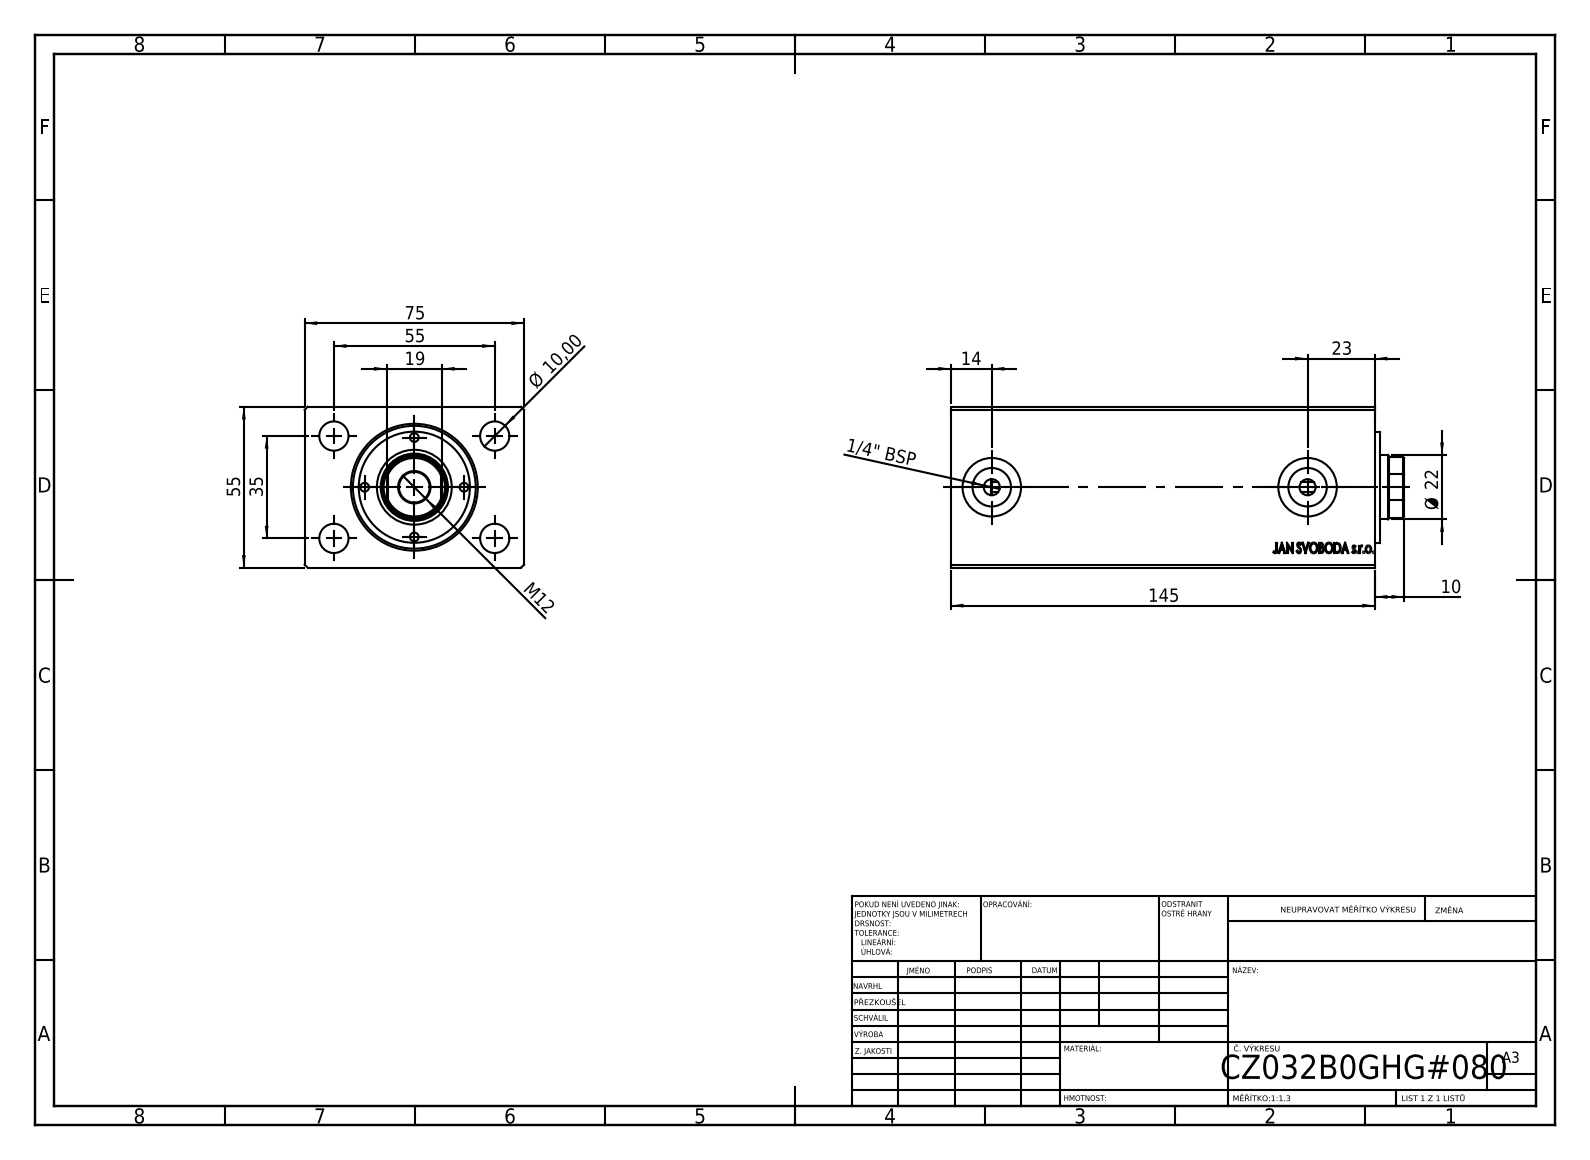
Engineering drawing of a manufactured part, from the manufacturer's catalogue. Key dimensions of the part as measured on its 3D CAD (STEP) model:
Part name (STEP PRODUCT): V500CZ; V500CZ_B_VC
STEP written by: SolidWorks 2019 (CONFIG_CONTROL_DESIGN)
Units: millimetres
Bodies: 3 solids, 875 faces (401 planar, 58 cylindrical, 416 other)
Overall size (bounding box): 155 × 75 × 55
Volume: 544 946 mm³ · Surface area: 84 002 mm²
Round holes (diameter × count): ⌀3 ×4, ⌀10 ×4, ⌀5.5 ×2, ⌀13.16 ×2, ⌀20 ×2, ⌀10.5 ×1, ⌀22 ×1, ⌀23 ×1, ⌀32 ×1, ⌀36 ×1, ⌀42 ×1
Round bosses / shafts (diameter × count): ⌀38 ×1
Partial cylindrical surfaces — rounded edges, fillets, slot ends (radius × count): R10.5 ×1
Main face-to-face distances: 55, 75, 145, 131.2, 13.8, 10, 13.6, 8.2, 1.8, 144.8
Hole centre spacings: 17, 20.41, 24.04, 27.5, 32.6, 44.12, 47.82, 34
